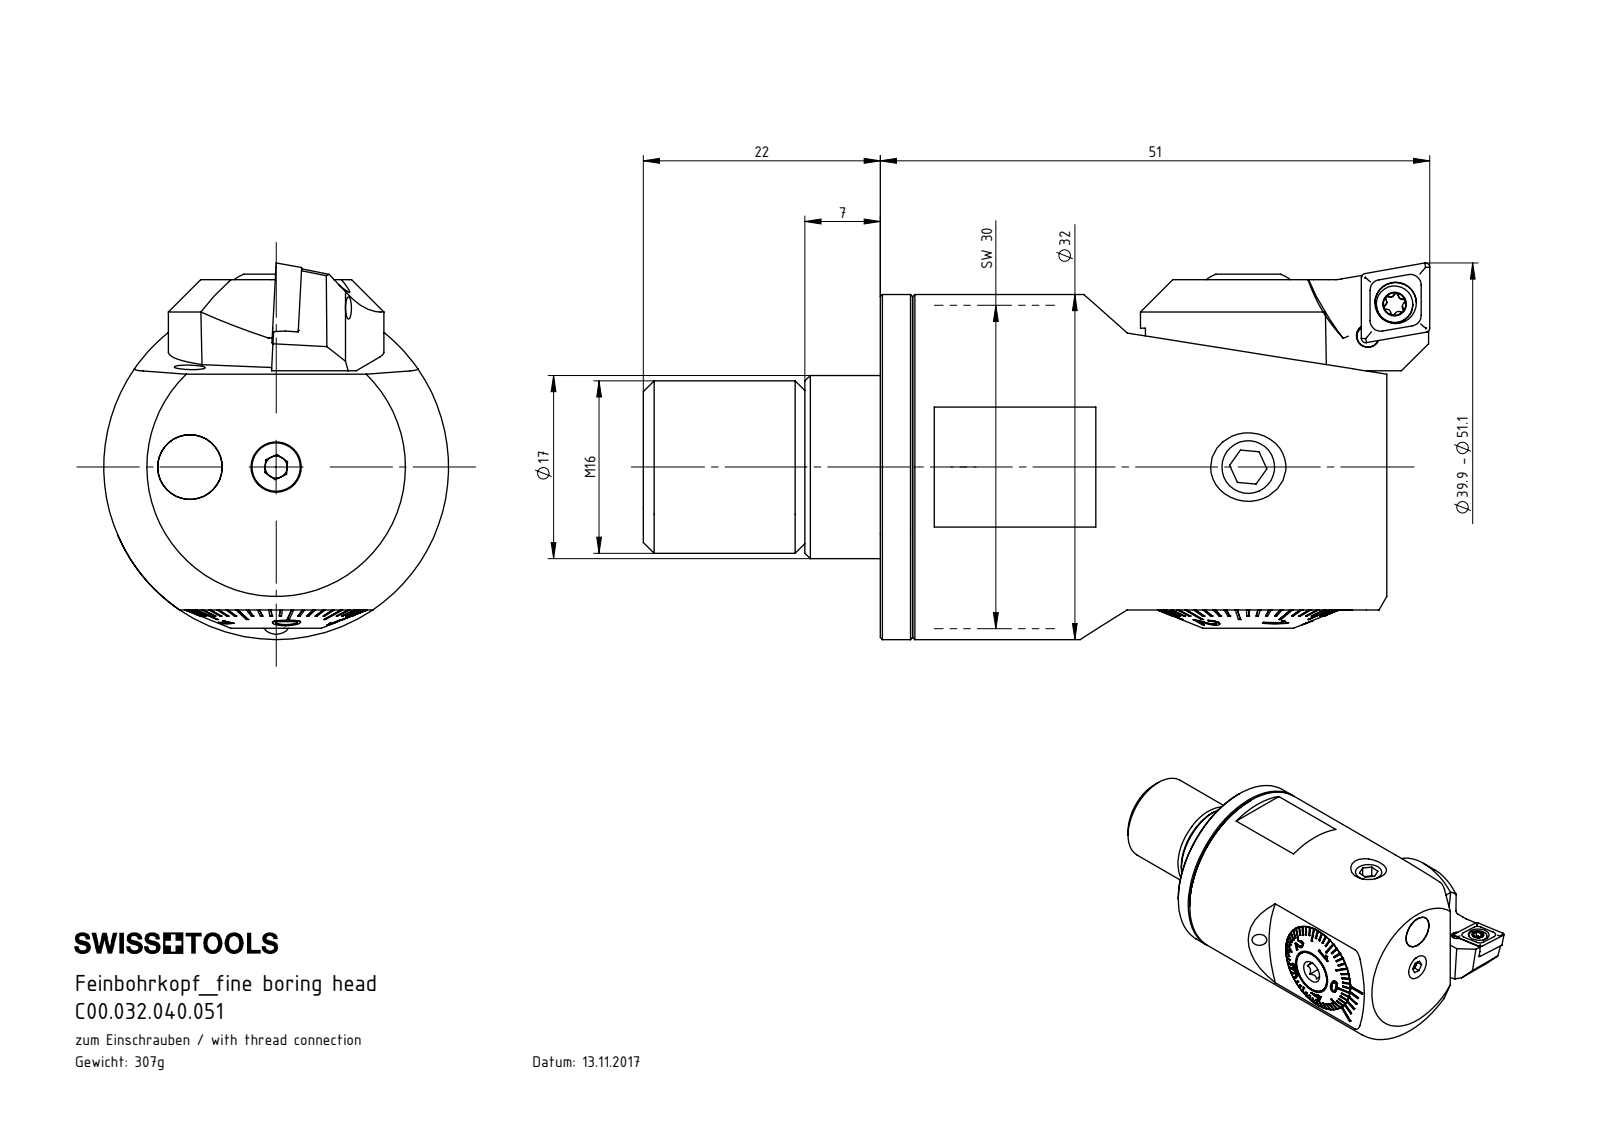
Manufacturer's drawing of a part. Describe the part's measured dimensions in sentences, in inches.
The part is named "HP5-F32.040.051_A; CCMT060204; F32; F32-BG1.010.006_A (+8 more)". Its 3-D file was written by "SolidWorks 2017 (CONFIG_CONTROL_DESIGN)". It is 20 solids with 837 faces: 363 planar, 158 cylindrical and 316 other. Overall it measures 2.874 by 1.376 by 1.26 inches. Its volume is 2.397 cubic inches and its surface area 31.43 square inches. Round holes: 5 of diameter 0.098, 2 of diameter 0.197, 2 of diameter 0.669, 1 of diameter 0.079, 1 of diameter 0.081, 1 of diameter 0.083, 1 of diameter 0.106, 1 of diameter 0.11, 1 of diameter 0.114, 1 of diameter 0.118, 1 of diameter 0.13, 1 of diameter 0.152. Round bosses or shafts: 2 of diameter 0.236, 2 of diameter 0.098, 1 of diameter 1.26, 1 of diameter 0.669, 1 of diameter 0.663, 1 of diameter 0.63, 1 of diameter 0.577, 1 of diameter 0.472. Partial cylindrical surfaces (rounded edges, fillets, slot ends): 6 of radius 0.008, 5 of radius 0.014, 4 of radius 0.02, 2 of radius 0.069, 1 of radius 0.014, 1 of radius 0.039, 1 of radius 0.042, 1 of radius 0.075. The main face-to-face distances are 0.118, 1.85, 1.732, 0.177, 0.99, 1.181, 0.315, 0.031, 0.059, 0.146. The hole center spacings are 0.151, 0.157, 0.224, 0.315, 0.46, 0.951.
